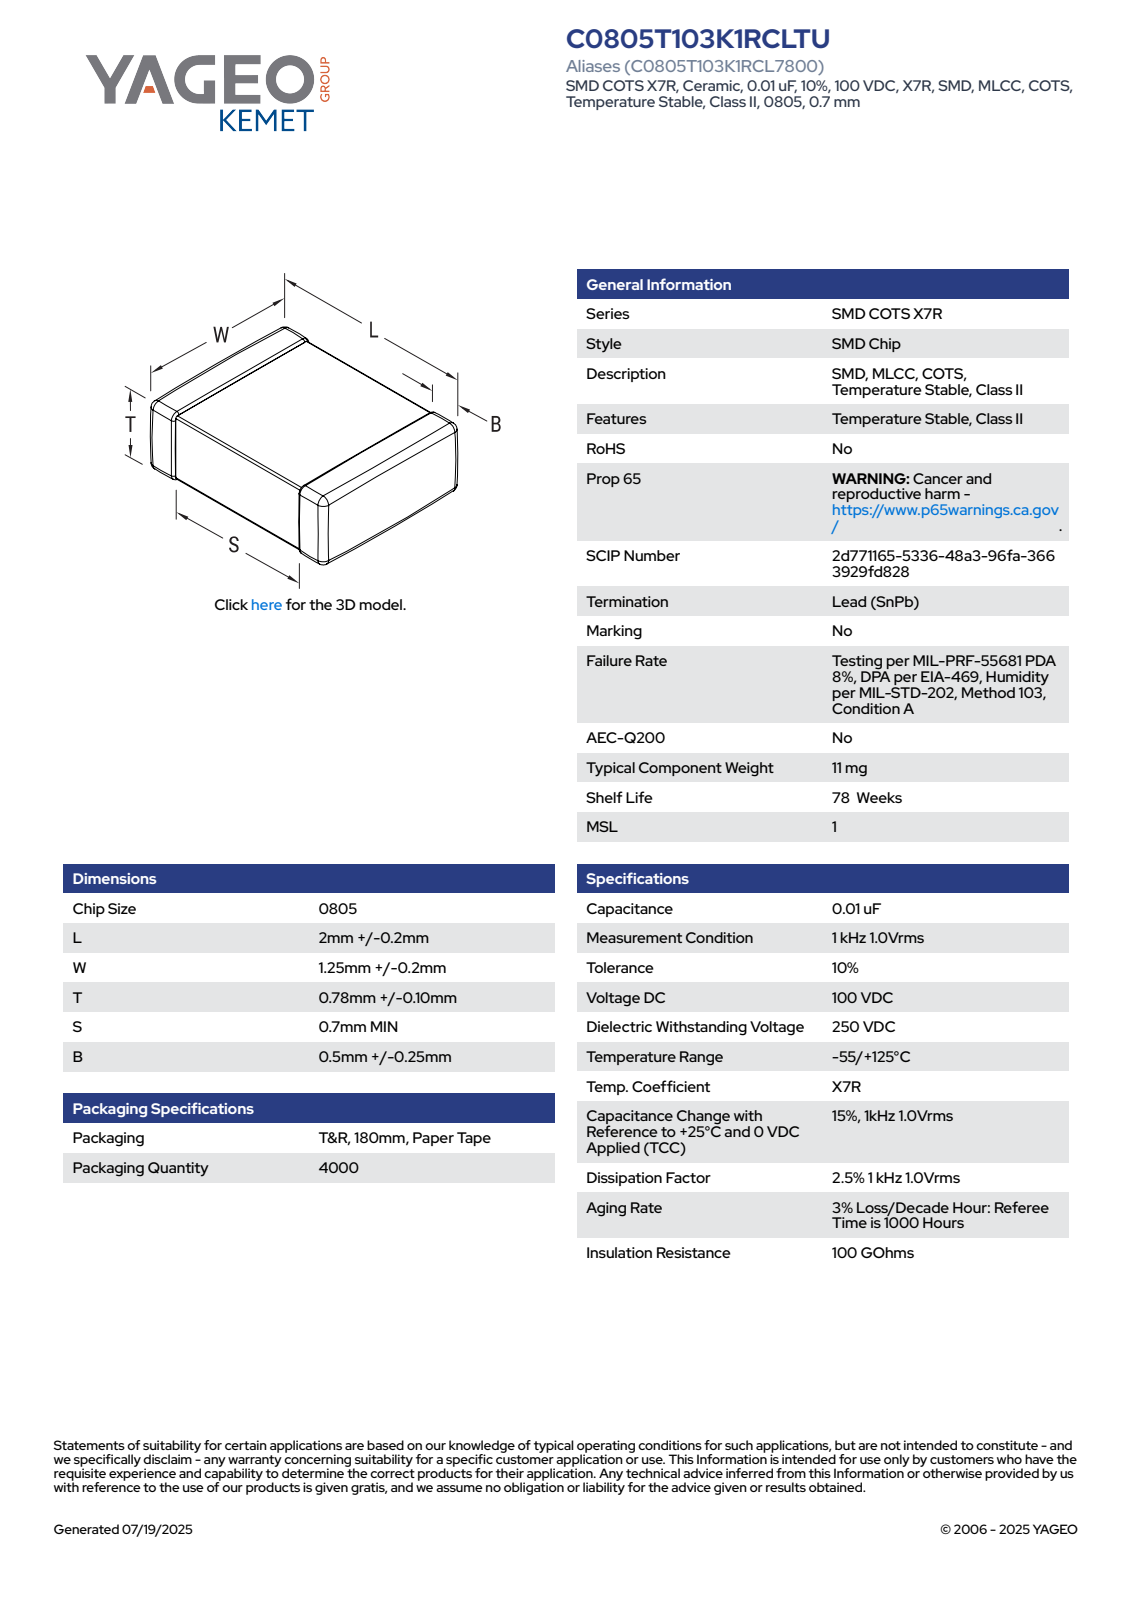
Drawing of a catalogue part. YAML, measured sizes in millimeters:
part_name: "CCSM_STD_0805_L2.2W1.45T0.88B0.75"
step_written_by: "SolidWorks 2014 (AUTOMOTIVE_DESIGN)"
units: millimeters
bodies: {solids: 4, faces: 125, planar: 71, cylindrical: 38, other: 16}
overall_size: [2.2, 1.45, 0.88]
volume: 3
surface_area: 13
face_to_face_distances: [0.85, 0.88, 2.2, 1.45, 1.42, 0.82, 1.39, 0.7, 0.72, 0.73]
